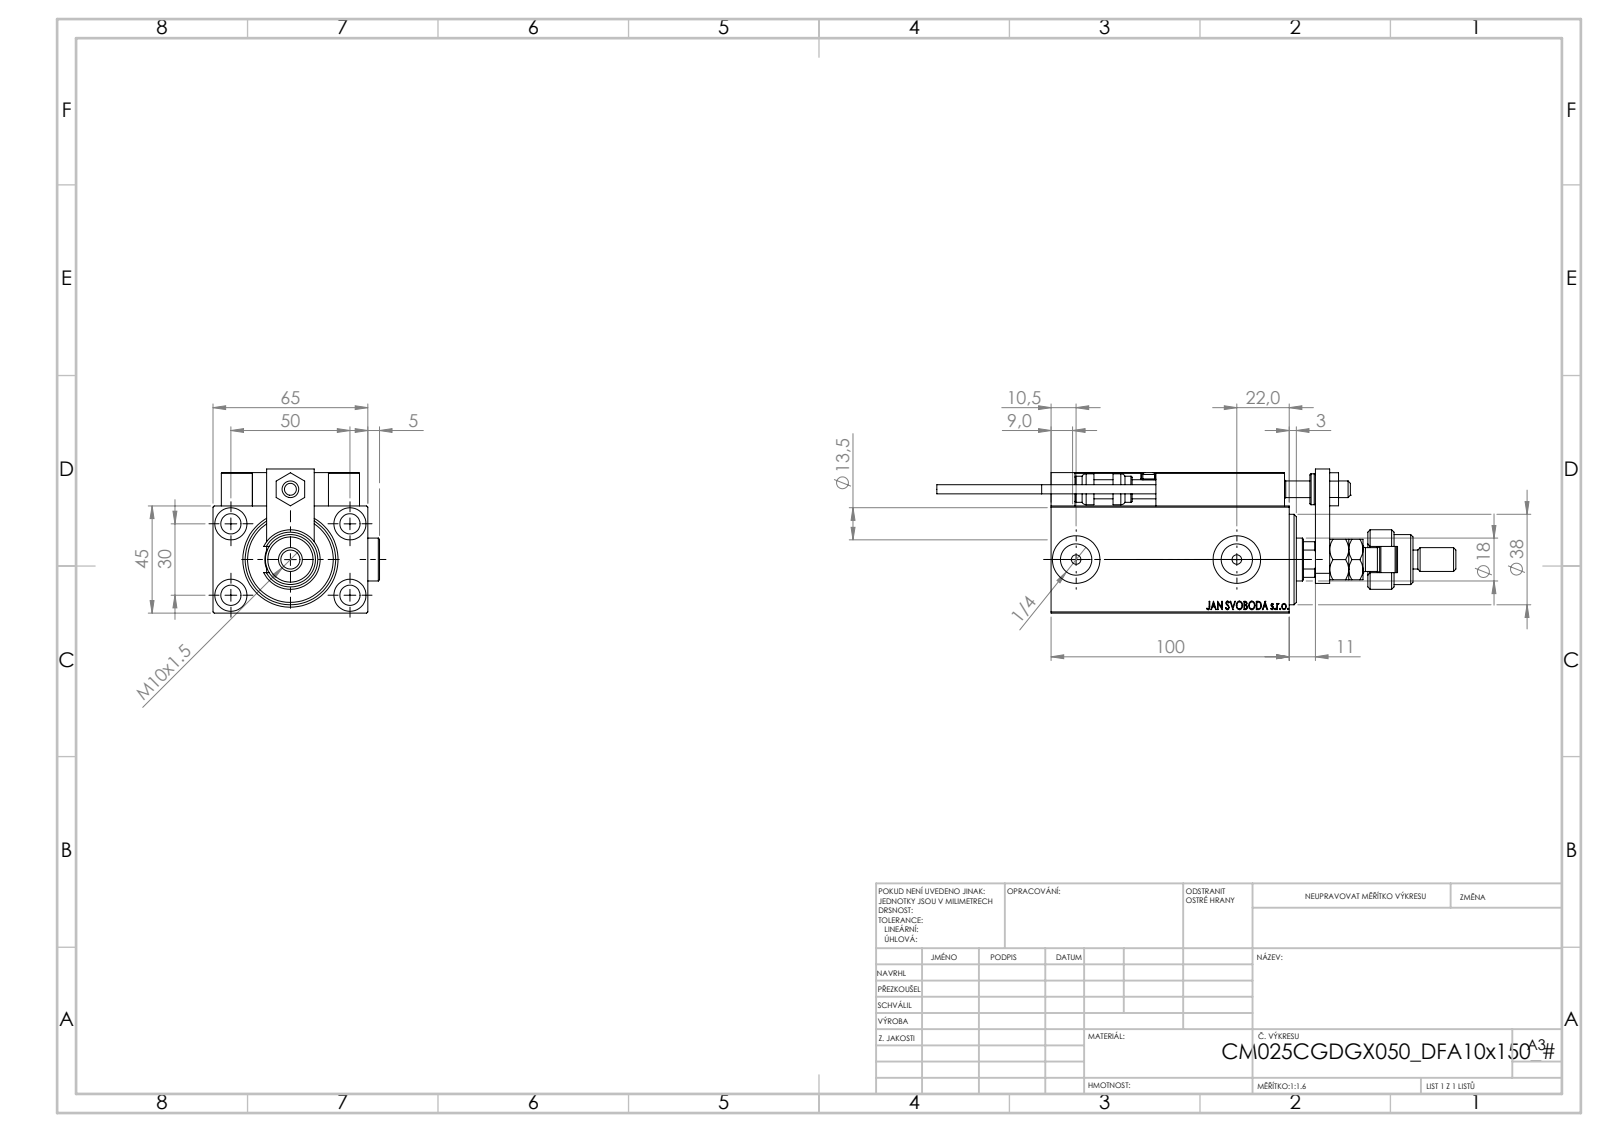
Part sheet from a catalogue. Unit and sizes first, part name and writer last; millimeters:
Units: millimetres
Overall size (bounding box): 218 × 69.9 × 60.5
Round holes (diameter × count): ⌀4 ×6, ⌀8 ×5, ⌀8.5 ×5, ⌀3.2 ×4, ⌀13.5 ×4, ⌀5 ×2, ⌀13.16 ×2, ⌀20 ×2, ⌀7 ×1, ⌀14.5 ×1, ⌀18 ×1, ⌀21.5 ×1
Round bosses / shafts (diameter × count): ⌀18 ×2, ⌀5 ×2, ⌀3.8 ×2, ⌀25 ×1, ⌀21 ×1, ⌀16 ×1, ⌀13 ×1, ⌀11 ×1
Partial cylindrical surfaces — rounded edges, fillets, slot ends (radius × count): R0.3 ×30, R3 ×2, R5.5 ×1, R8.5 ×1, R8.75 ×1
Main face-to-face distances: 45, 65, 14, 6, 59, 3, 5, 13, 7, 89
Hole centre spacings: 29.15, 11.37, 20, 28.9, 29.59, 29.69, 30, 36.06
Volume: 308 771 mm³ · Surface area: 92 096 mm²
Bodies: 27 solids, 1421 faces (622 planar, 217 cylindrical, 582 other)
Part name (STEP PRODUCT): KONCOVKA; V450CM_C_VCP; ALLEN BOLT D8; MAGNET (+7 more)
STEP written by: SolidWorks 2019 (CONFIG_CONTROL_DESIGN)
